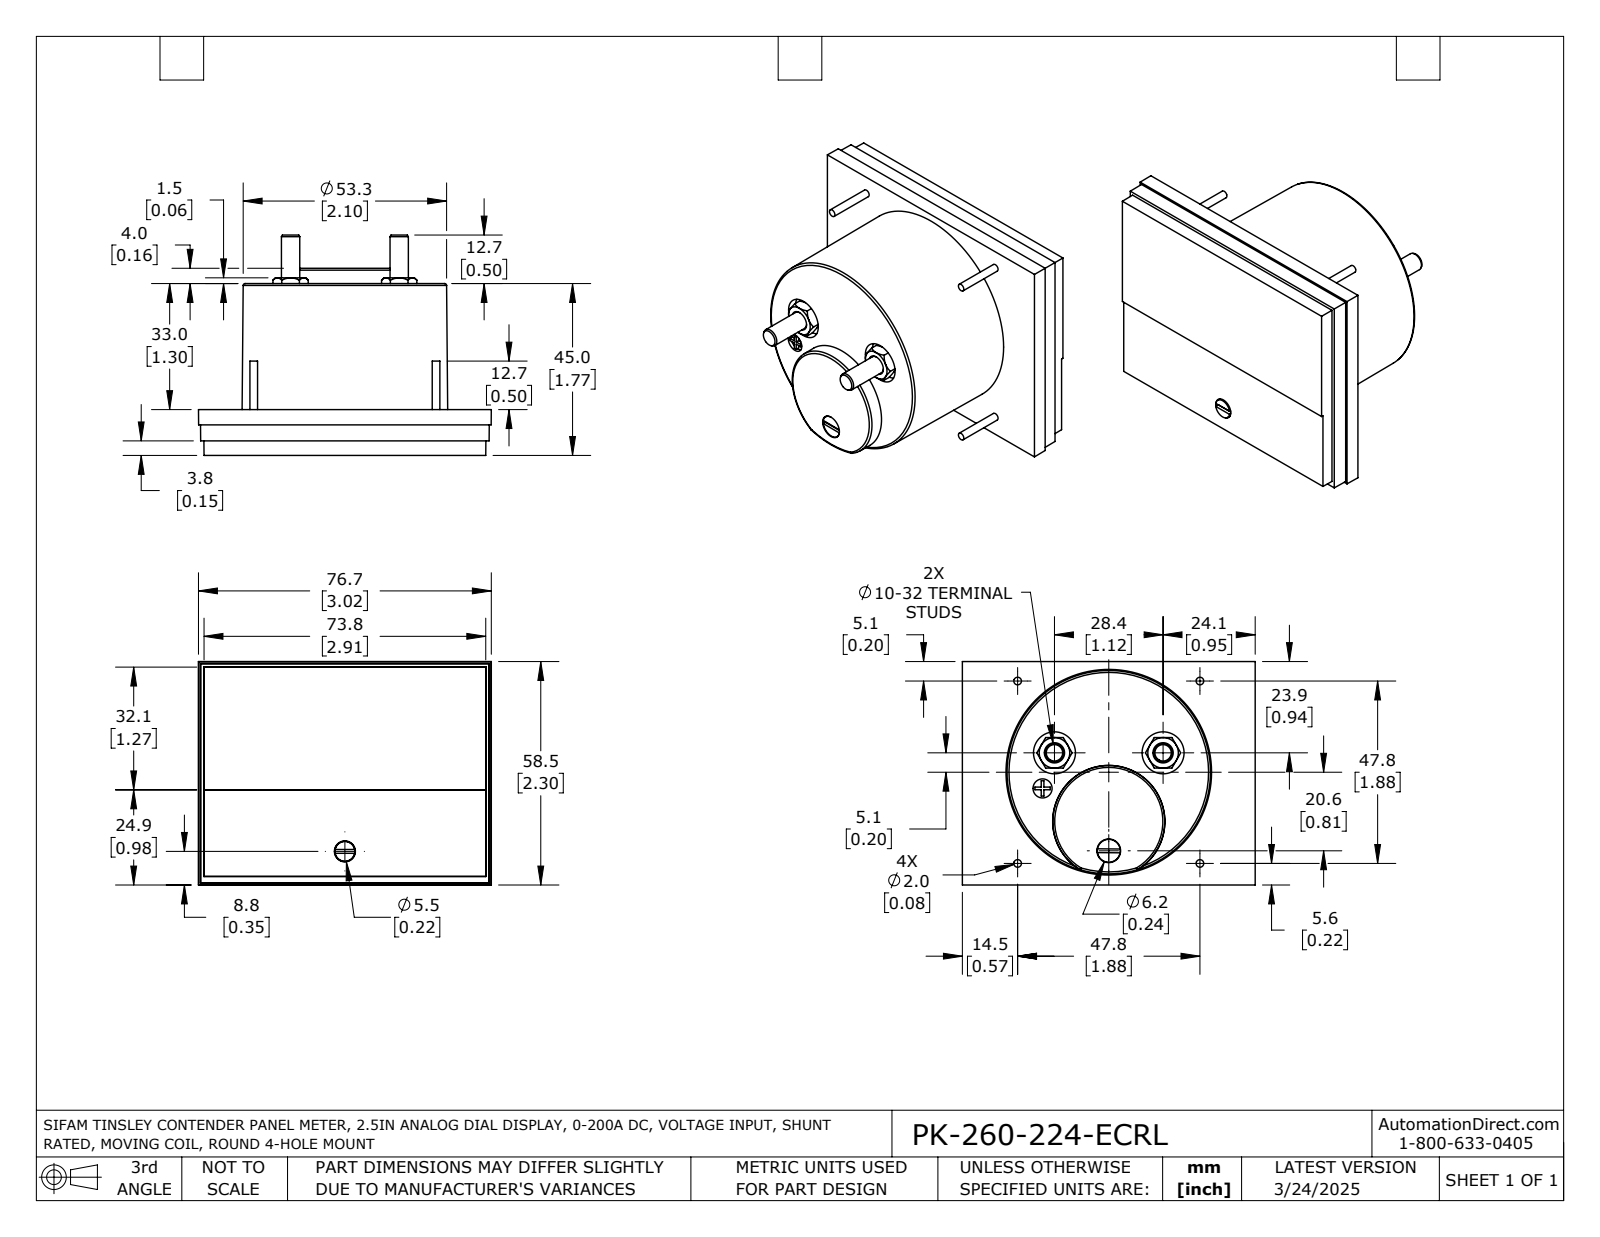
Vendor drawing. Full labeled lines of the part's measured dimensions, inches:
Part name (STEP PRODUCT): PK-260-224-ECRL
STEP written by: SolidWorks 2021 (AUTOMOTIVE_DESIGN)
Units: inches
Bodies: 1 solid, 192 faces (95 planar, 37 cylindrical, 60 other)
Overall size (bounding box): 3.02 × 2.303 × 2.272
Volume: 7.657 in³ · Surface area: 36.55 in²
Round holes (diameter × count): ⌀0.197 ×3, ⌀0.433 ×2, ⌀0.209 ×1, ⌀0.217 ×1, ⌀0.244 ×1
Round bosses / shafts (diameter × count): ⌀0.079 ×4, ⌀0.189 ×2, ⌀0.236 ×1, ⌀0.205 ×1
Partial cylindrical surfaces — rounded edges, fillets, slot ends (radius × count): R0.033 ×1
Main face-to-face distances: 0.02, 0.472, 0.13, 0.322, 0.15, 0.453, 0.057, 0.077, 0.396, 0.073
Hole centre spacings: 1.155, 1.16, 0.387, 0.938, 0.942, 1.12, 1.295
